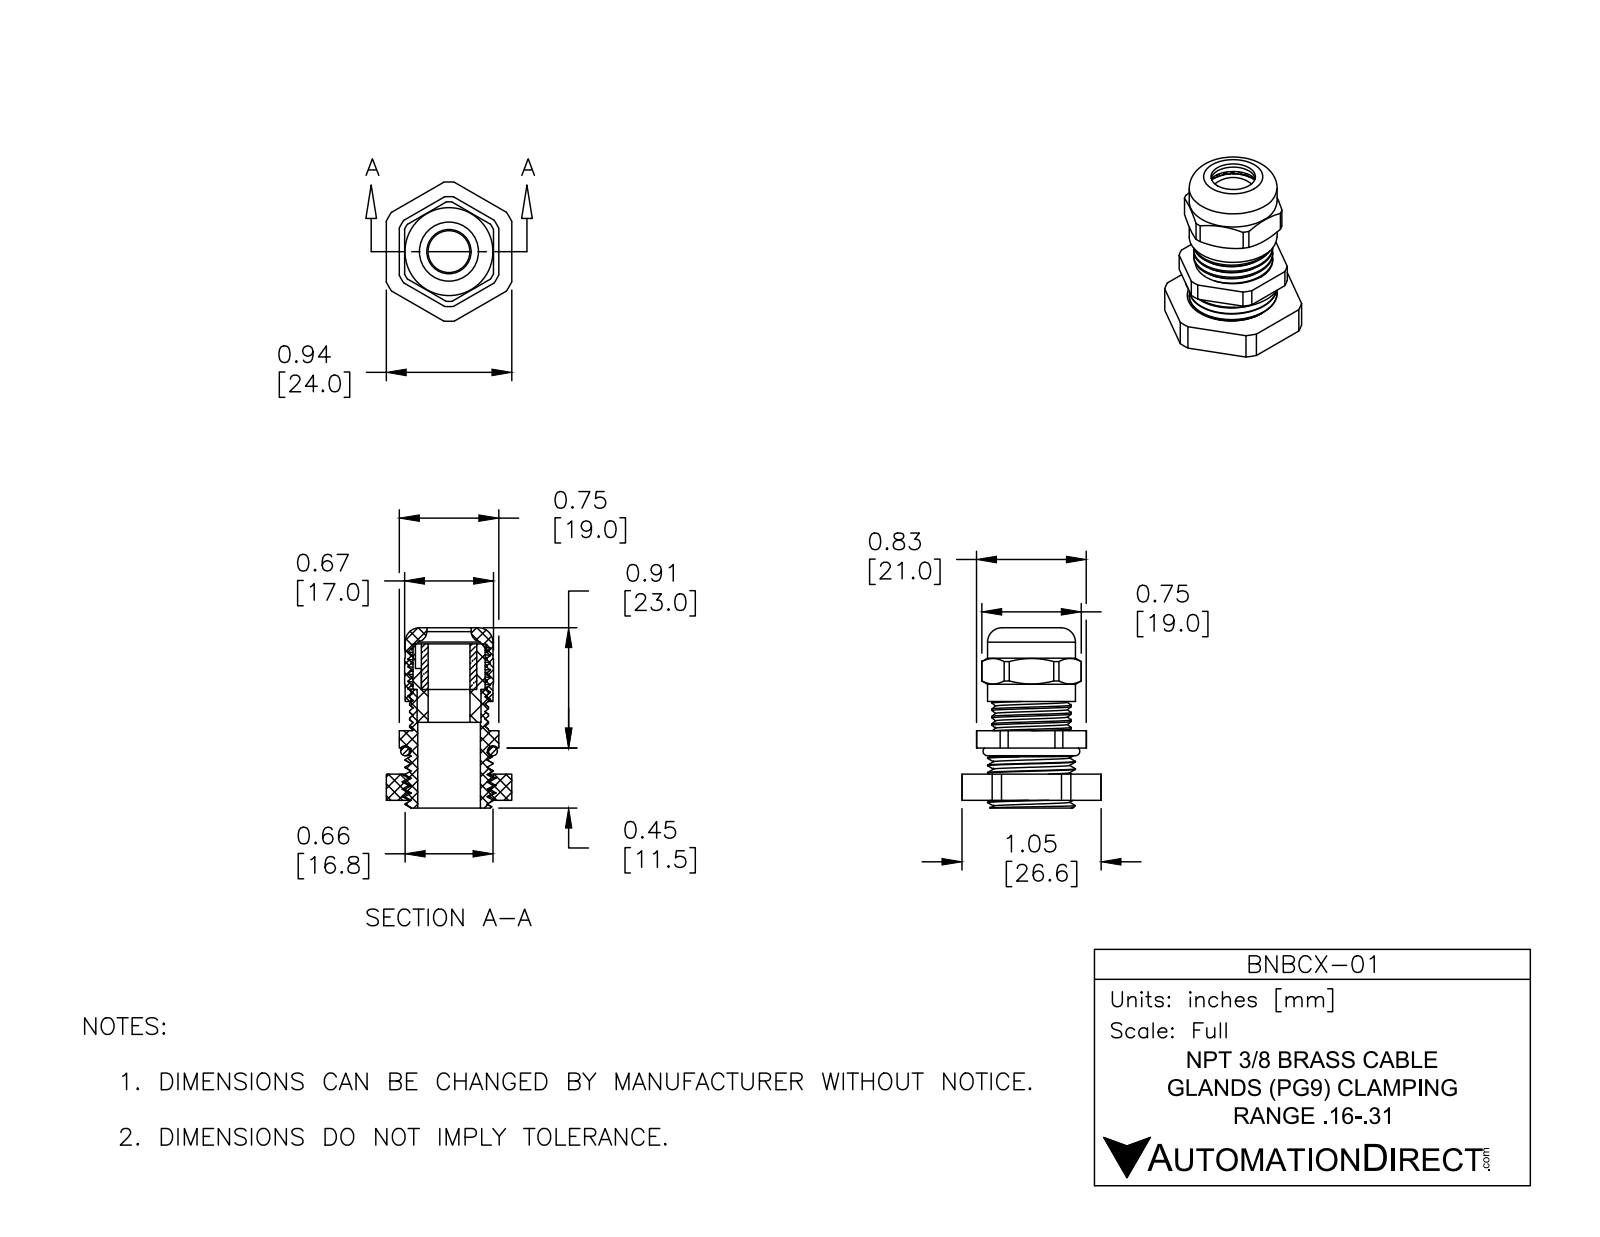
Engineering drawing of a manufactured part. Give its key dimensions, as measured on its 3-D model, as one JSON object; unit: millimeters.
{"part_name": "BNBCX-01", "step_written_by": "SolidWorks 2015 (CONFIG_CONTROL_DESIGN)", "units": "millimeters", "bodies": {"solids": 6, "faces": 262, "planar": 134, "cylindrical": 91, "other": 37}, "overall_size": [34.47, 26.6, 24], "volume_mm3": 5669, "surface_area_mm2": 8761, "round_holes": [[8, 1], [8.48, 1], [10.6, 1], [11.98, 1], [12.2, 1], [14.43, 1], [15.66, 1]], "round_bosses_or_shafts": [[16.8, 1], [16.79, 1], [15.1, 1], [13.8, 1]], "partial_cylinders_radius": [[9.5, 1], [10.5, 1], [13.3, 1]], "face_to_face_distances": [5, 20.5, 3.5, 0.5, 2.5, 21.5, 1, 18, 24, 21.18]}
